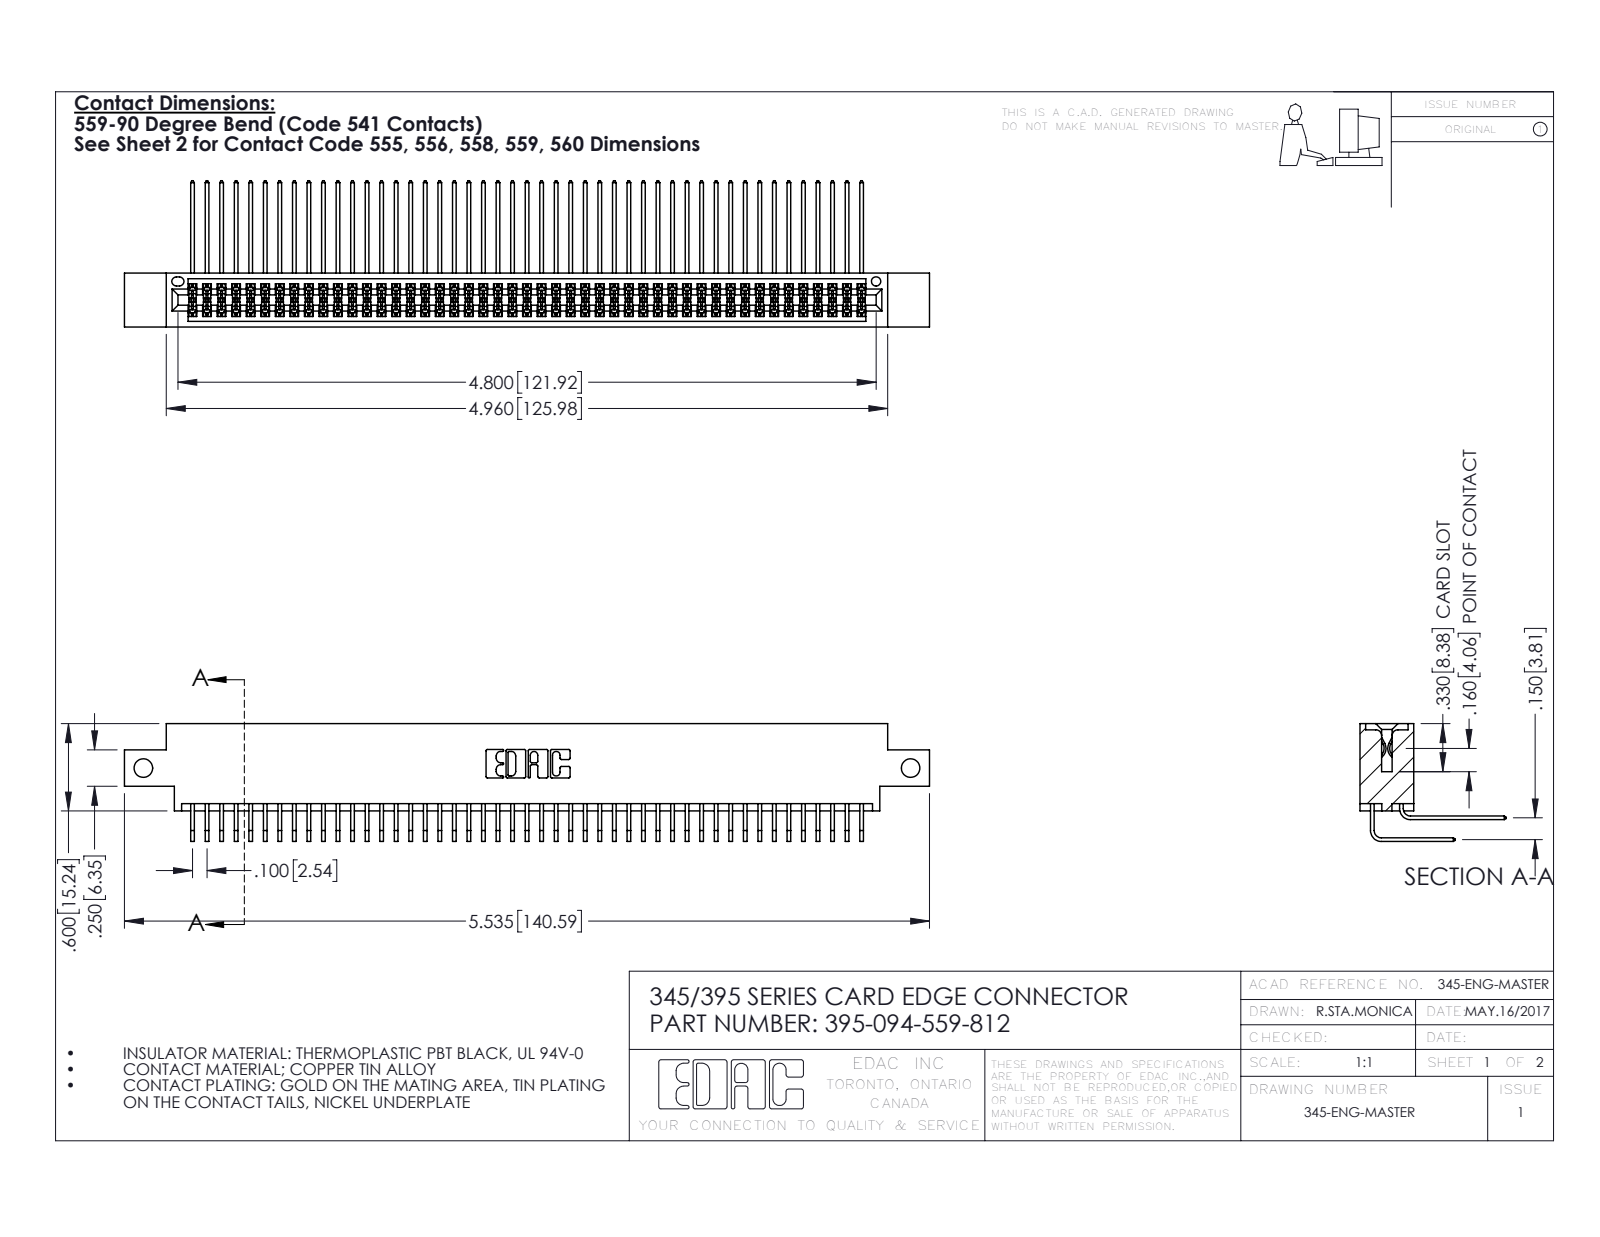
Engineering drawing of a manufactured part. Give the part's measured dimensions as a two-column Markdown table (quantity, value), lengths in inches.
| quantity | value |
| --- | --- |
| part name | 345-292-001_559 Tail - 2; 345 Part_0.170 Offset - Side Mount; 345-292-001_558 559 Tail - 1; 395-094-559-812 |
| STEP written by | SolidWorks 2016 (CONFIG_CONTROL_DESIGN) |
| units | inches |
| bodies | 95 solids, 5018 faces (3374 planar, 1644 cylindrical, 0 other) |
| overall size | 5.535 × 1.005 × 0.809 |
| volume | 0.857 in³ |
| surface area | 36.29 in² |
| round holes (diameter × count) | 0.128 × 2, 0.064 × 1 |
| partial cylindrical surfaces (radius × count) | 0.006 × 141, 0.01 × 22, 0.007 × 6, 0.031 × 6, 0.026 × 3, 0.014 × 2, 0.019 × 2, 0.022 × 2 |
| main face-to-face distances | 0.072, 0.298, 0.37, 0.2, 0.098, 0.272, 0.025, 0.225, 0.175, 0.15 |
| hole center spacings | 5.275 |
